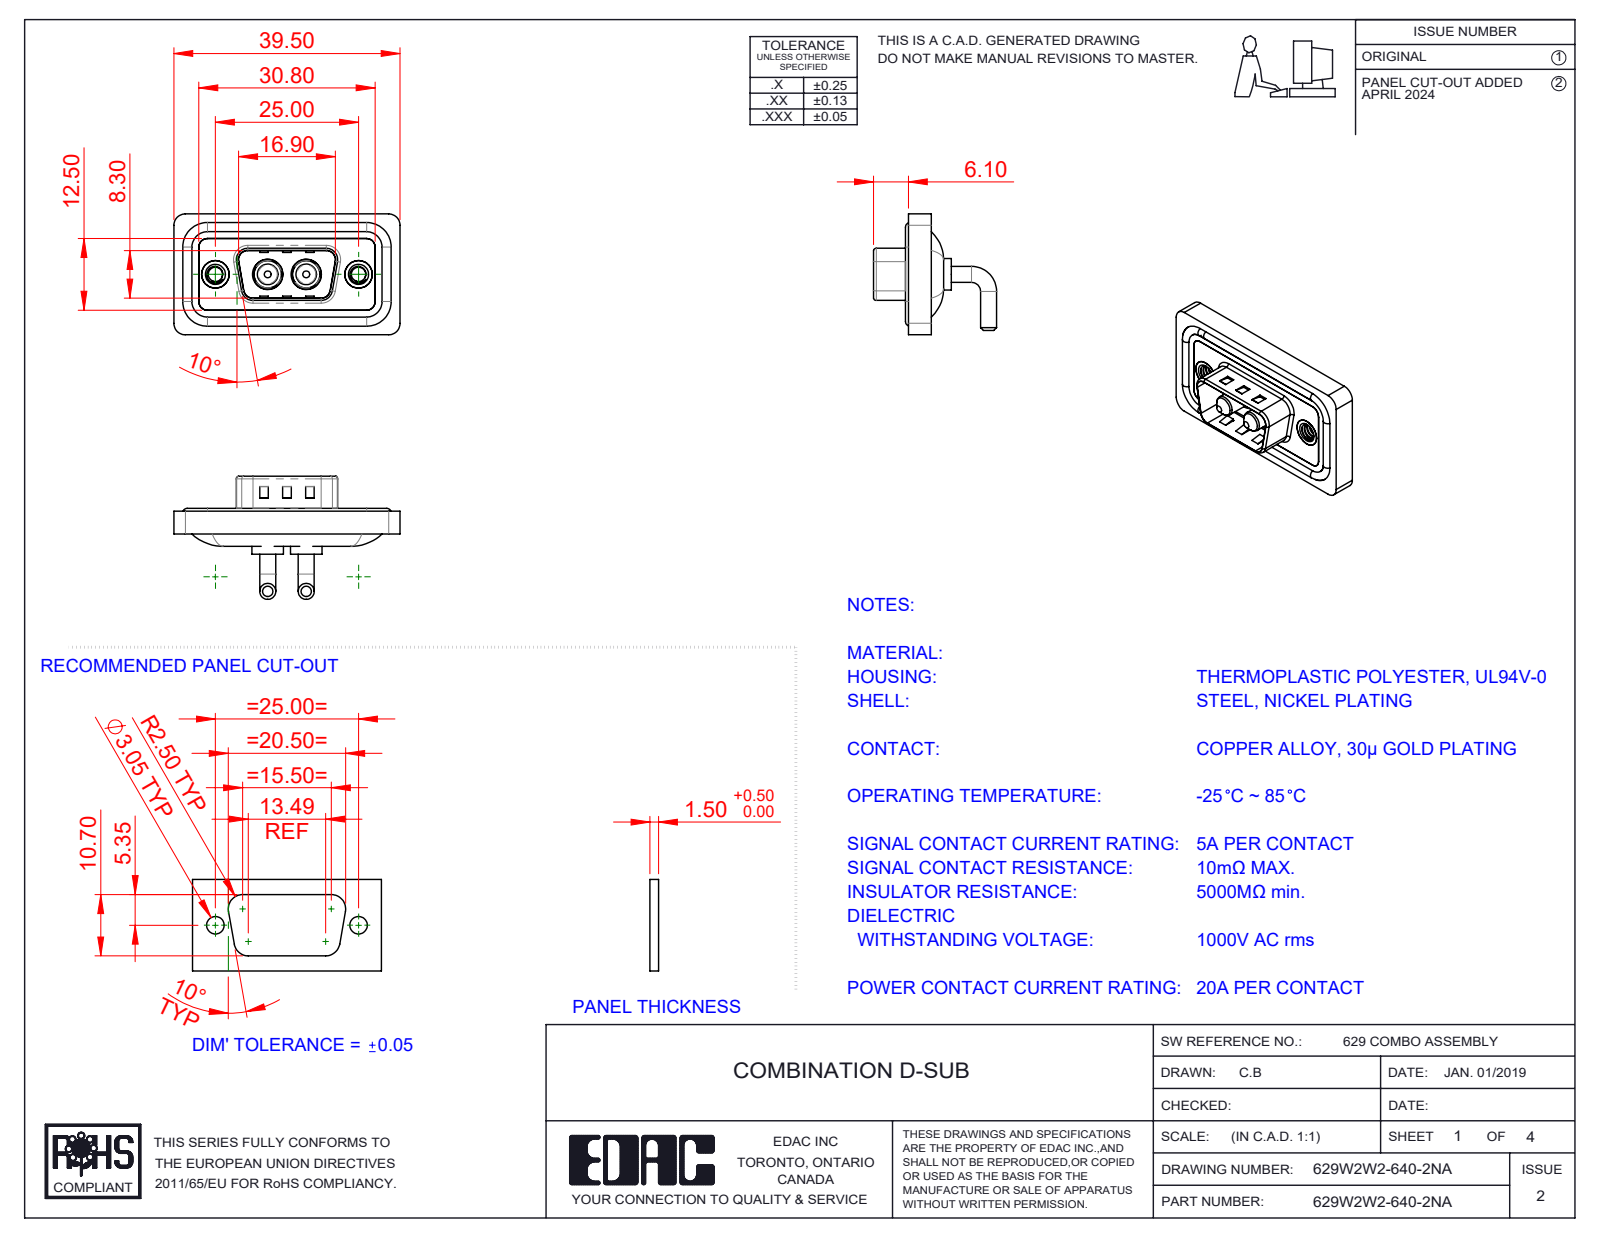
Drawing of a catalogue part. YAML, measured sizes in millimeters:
part_name: "629Combo Waterproof Housing_09 Contacts; 629Combo Shell Rear_09 Contacts; 629Combo Shell Front_09 Contacts; 629W2W2-640-2NA (+3 more)"
step_written_by: "SolidWorks 2023 (CONFIG_CONTROL_DESIGN)"
units: millimeters
bodies: {solids: 11, faces: 491, planar: 165, cylindrical: 220, other: 106}
overall_size: [39.5, 21.5, 21.1]
volume: 4588
surface_area: 7171
round_holes:
  - {diameter: 2.5, count: 2}
  - {diameter: 4, count: 2}
  - {diameter: 4.8, count: 2}
  - {diameter: 4.85, count: 2}
  - {diameter: 5, count: 2}
  - {diameter: 5.3, count: 2}
round_bosses_or_shafts:
  - {diameter: 2.8, count: 4}
  - {diameter: 1.6, count: 4}
  - {diameter: 5.5, count: 2}
  - {diameter: 5.2, count: 2}
  - {diameter: 4.9, count: 2}
  - {diameter: 4.75, count: 2}
  - {diameter: 3.75, count: 2}
  - {diameter: 3.6, count: 2}
partial_cylinders:
  - {radius: 1.5, count: 18}
  - {radius: 2, count: 18}
  - {radius: 0.5, count: 8}
  - {radius: 1.6, count: 8}
  - {radius: 0.25, count: 4}
  - {radius: 0.6, count: 4}
  - {radius: 0.65, count: 4}
  - {radius: 0.9, count: 4}
face_to_face_distances: [0.4, 2.9, 1.1, 0.8, 2.1, 2.5, 3.1, 1.6, 4.5, 1.5]
hole_center_spacings: [9.14, 15.86, 6.72, 25]
